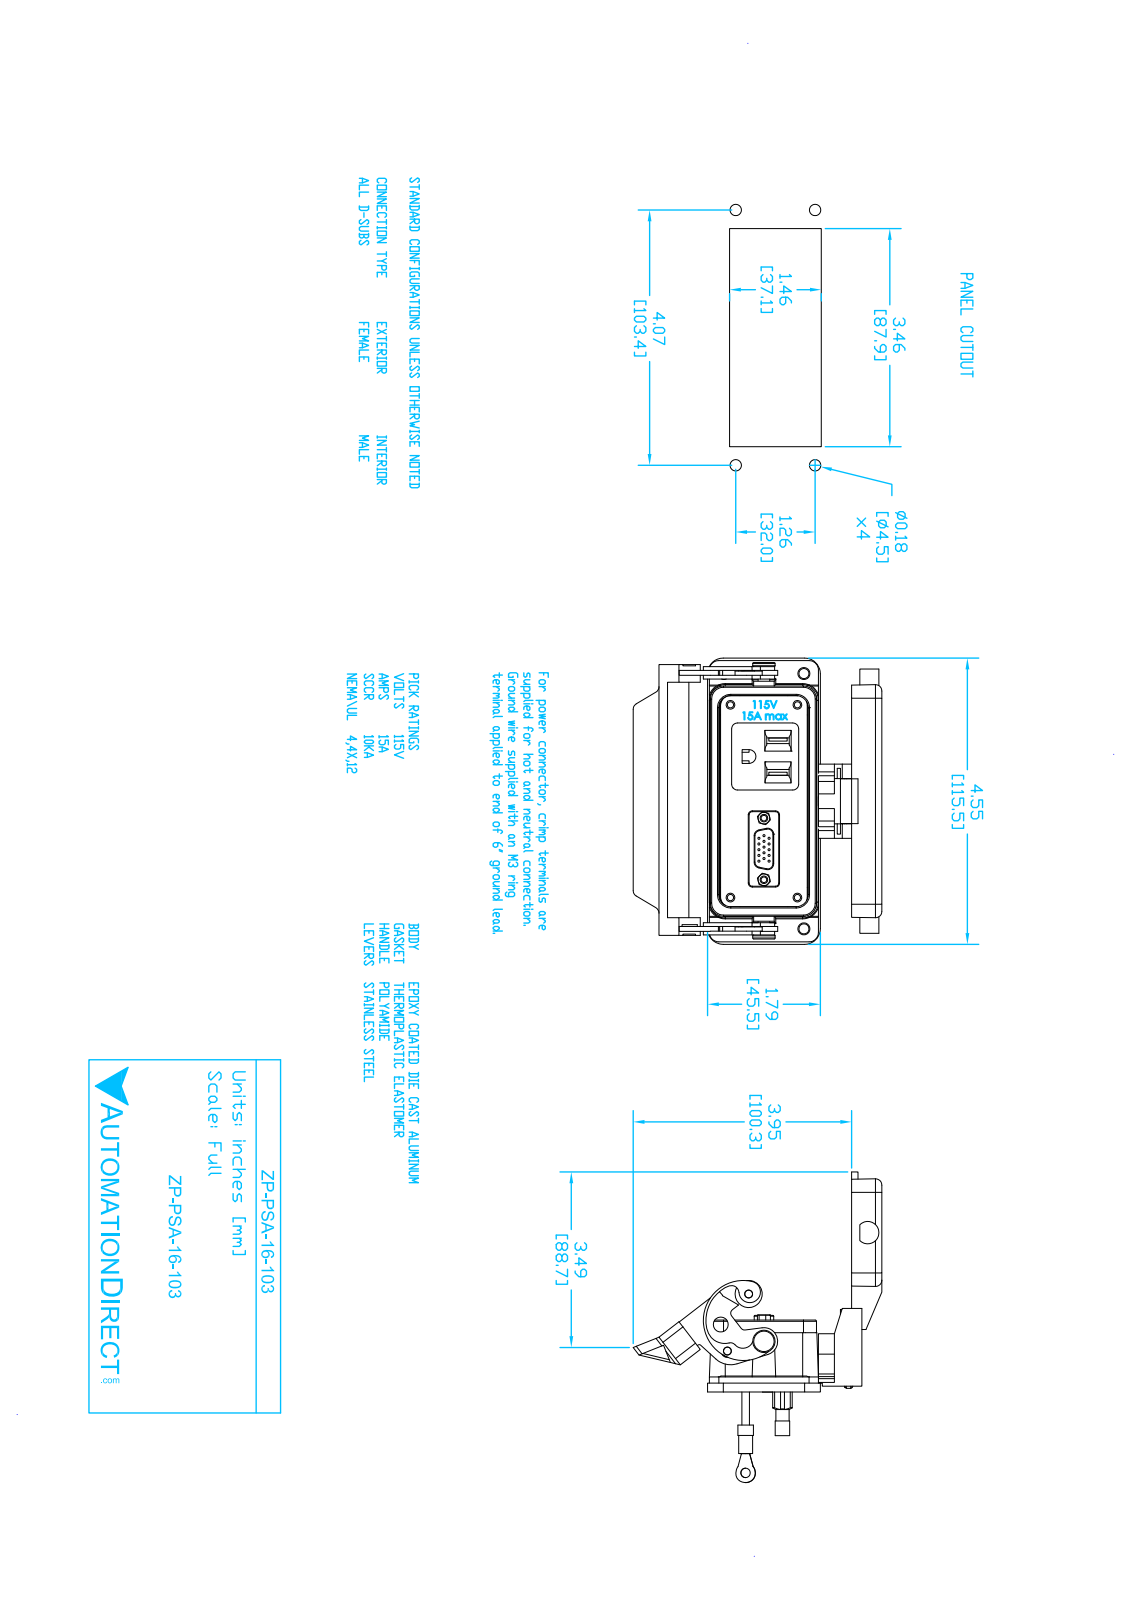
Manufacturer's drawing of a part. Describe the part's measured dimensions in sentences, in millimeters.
The part is named "ZP-PSA-16-103". Its 3-D file was written by "SolidWorks 2017 (AUTOMOTIVE_DESIGN)". It is 1 solid with 1861 faces: 1006 planar, 502 cylindrical and 353 other. Overall it measures 125 by 115.5 by 100.8 millimeters. Its volume is 99 960 cubic millimeters and its surface area 68 000 square millimeters. Round holes: 15 of diameter 0.8, 6 of diameter 4.1, 5 of diameter 4.8, 4 of diameter 2.5, 4 of diameter 3.7, 3 of diameter 3.2, 2 of diameter 2.3, 2 of diameter 3, 2 of diameter 3.1, 2 of diameter 3.4, 2 of diameter 3.8, 2 of diameter 5.1. Round bosses or shafts: 15 of diameter 1, 4 of diameter 5.7, 4 of diameter 5.6, 4 of diameter 3, 2 of diameter 5.8, 2 of diameter 5.3, 2 of diameter 4.7, 2 of diameter 2.8. Partial cylindrical surfaces (rounded edges, fillets, slot ends): 16 of radius 2.5, 13 of radius 3.8, 12 of radius 0.8, 10 of radius 0.5, 9 of radius 0.4, 8 of radius 0.1, 8 of radius 0.6, 8 of radius 2.4. The main face-to-face distances are 1.5, 3.4, 0.5, 17.1, 18.6, 2.9, 9.3, 103.3, 1.5, 4.8. The hole center spacings are 2.7, 3, 5.3, 5.1, 2.6, 5.1, 4.3, 6.1.
